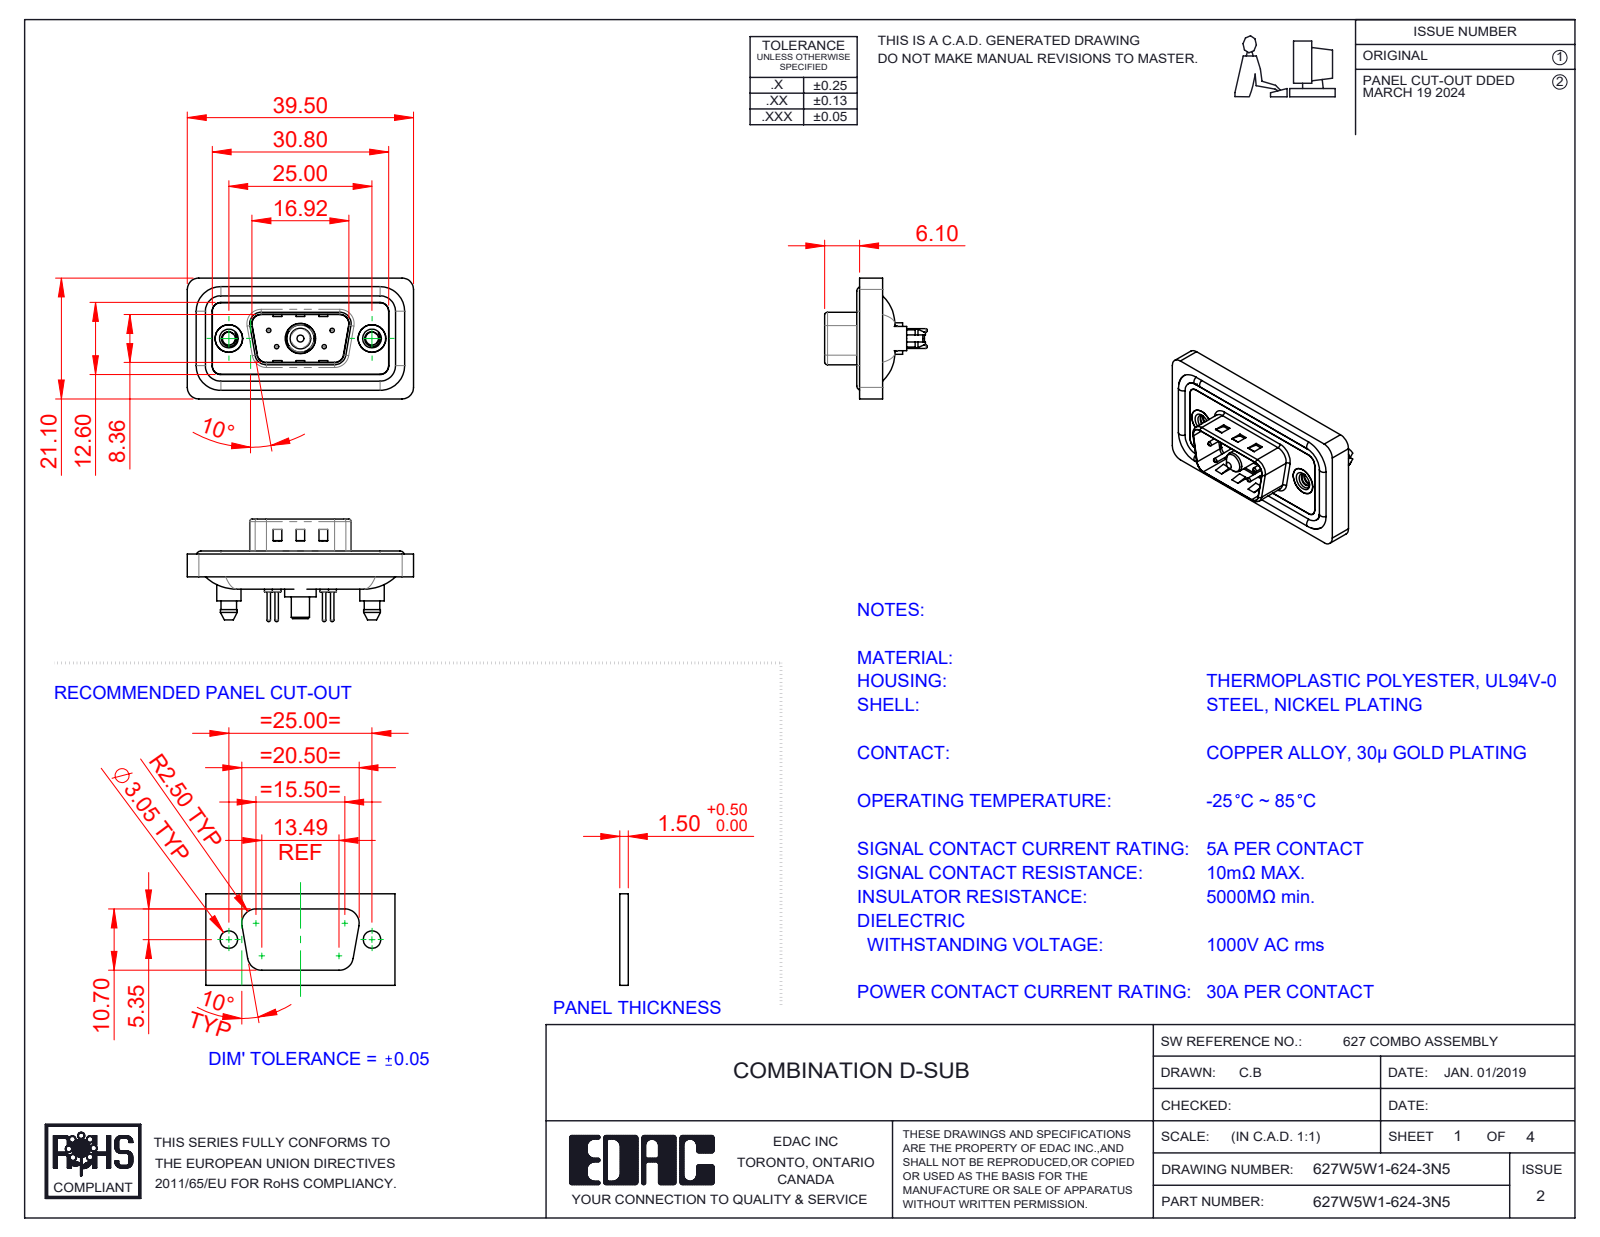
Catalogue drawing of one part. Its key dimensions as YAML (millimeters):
part_name: "627Combo Threaded Boardlock_5; 627Combo Contact Row 2_24; 627Combo Contact Row 1_24; 627Combo Shell Front_09 Contacts (+5 more)"
step_written_by: "SolidWorks 2023 (CONFIG_CONTROL_DESIGN)"
units: millimeters
bodies: {solids: 13, faces: 648, planar: 199, cylindrical: 287, other: 162}
overall_size: [39.5, 21.1, 17.9]
volume: 4528
surface_area: 7279
round_holes:
  - {diameter: 0.75, count: 4}
  - {diameter: 1.6, count: 4}
  - {diameter: 2, count: 4}
  - {diameter: 2.26, count: 2}
  - {diameter: 4, count: 2}
  - {diameter: 4.8, count: 2}
  - {diameter: 5, count: 2}
  - {diameter: 4.85, count: 1}
  - {diameter: 5.3, count: 1}
round_bosses_or_shafts:
  - {diameter: 1.6, count: 4}
  - {diameter: 1.5, count: 4}
  - {diameter: 0.6, count: 4}
  - {diameter: 5.4, count: 2}
  - {diameter: 4.9, count: 2}
  - {diameter: 4.25, count: 2}
  - {diameter: 5.5, count: 1}
  - {diameter: 5.2, count: 1}
partial_cylinders:
  - {radius: 1.5, count: 24}
  - {radius: 2, count: 18}
  - {radius: 1.6, count: 10}
  - {radius: 0.5, count: 8}
  - {radius: 0.25, count: 4}
  - {radius: 0.6, count: 4}
  - {radius: 0.65, count: 4}
  - {radius: 0.9, count: 4}
face_to_face_distances: [0.4, 1.1, 2.9, 1.6, 1.5, 3.1, 0.5, 2.5, 4, 0.8]
hole_center_spacings: [3.16, 5.72, 7.1, 12.5, 18.1, 4.39, 4.4, 8.31]
